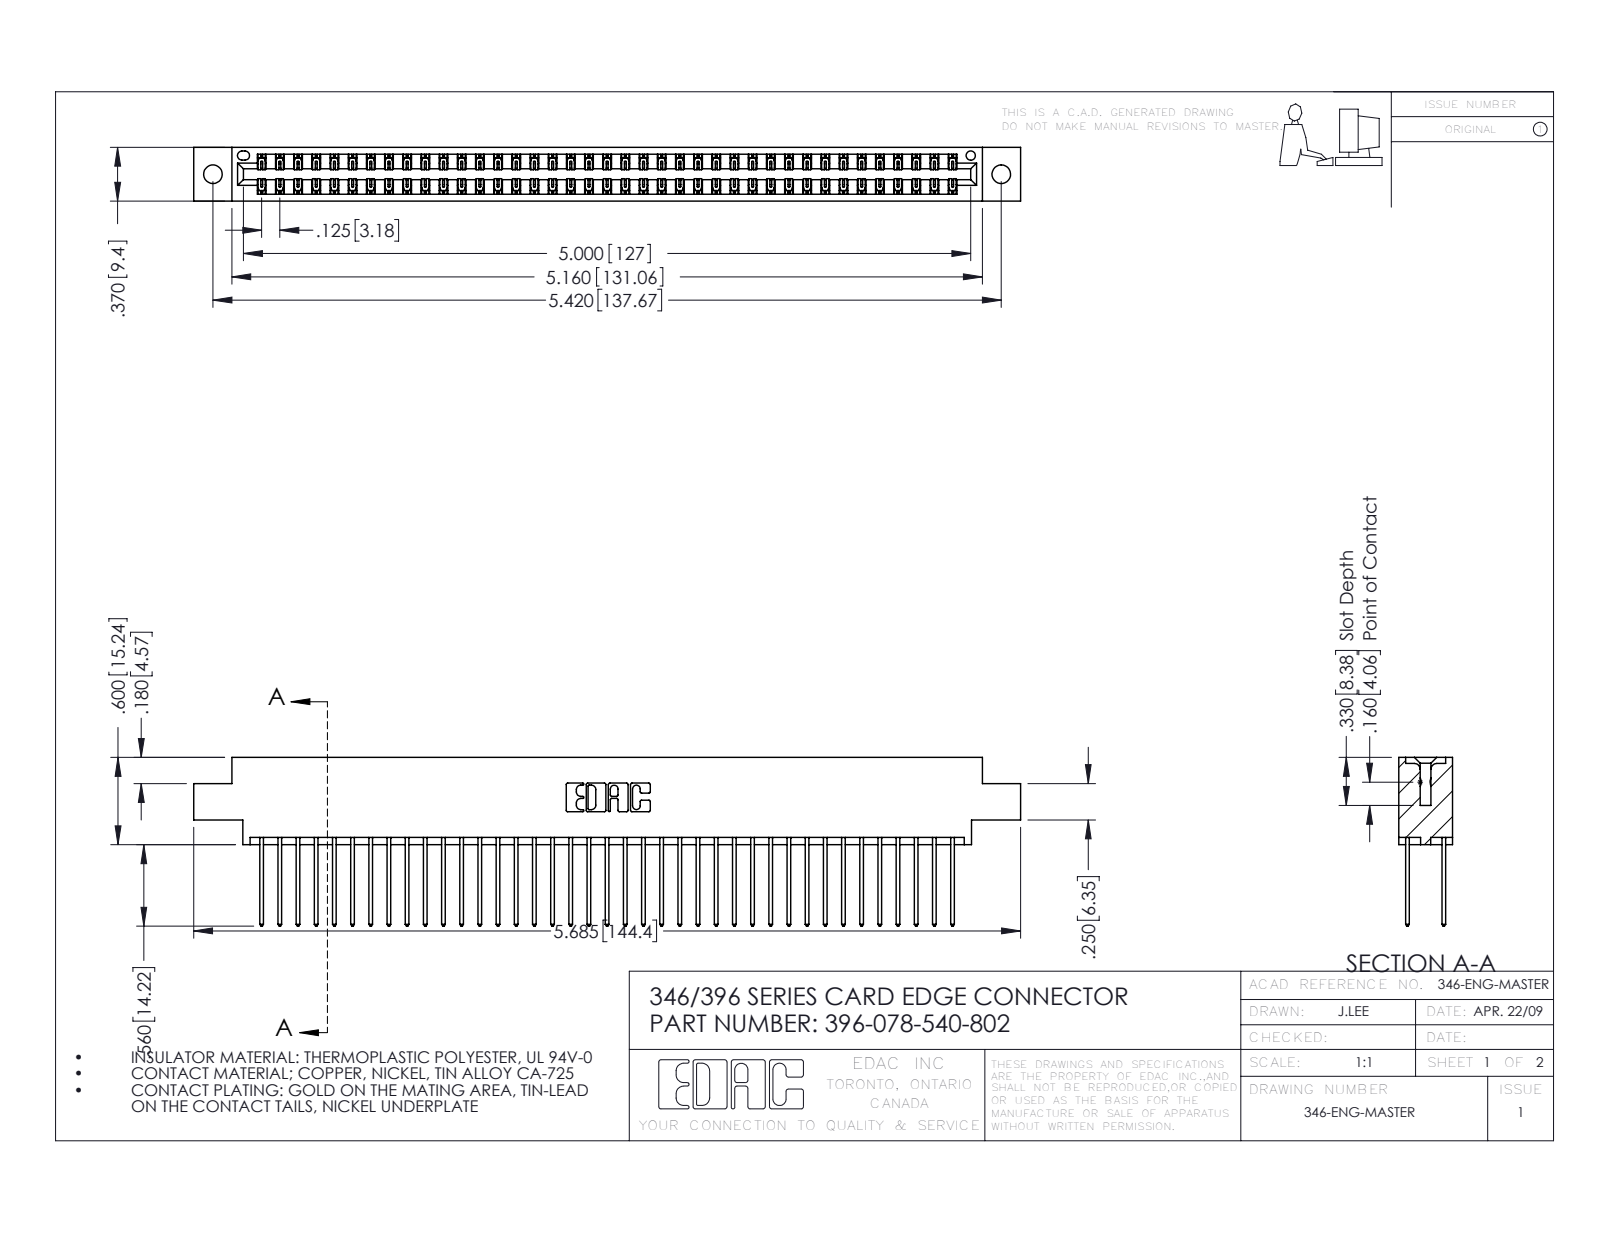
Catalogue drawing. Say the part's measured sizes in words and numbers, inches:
The part is named "346 Part_0.170 Offset - 0.128 Dia; 396-078-540-802; 345-292-001_345-293-140". Its 3-D file was written by "SolidWorks 2016 (CONFIG_CONTROL_DESIGN)". It is 79 solids with 4182 faces: 2810 planar, 1372 cylindrical and 0 other. Overall it measures 5.685 by 1.16 by 0.37 inches. Its volume is 0.864 cubic inches and its surface area 32.13 square inches. Round holes: 2 of diameter 0.128, 1 of diameter 0.064. Partial cylindrical surfaces (rounded edges, fillets, slot ends): 117 of radius 0.006, 78 of radius 0.01, 22 of radius 0.01, 6 of radius 0.007, 6 of radius 0.031, 3 of radius 0.026, 2 of radius 0.014, 2 of radius 0.022. The main face-to-face distances are 0.048, 0.322, 0.25, 0.072, 0.298, 0.025, 0.37, 0.275, 0.148, 0.222. The hole center spacings are 0.246, 5.211, 5.42.
